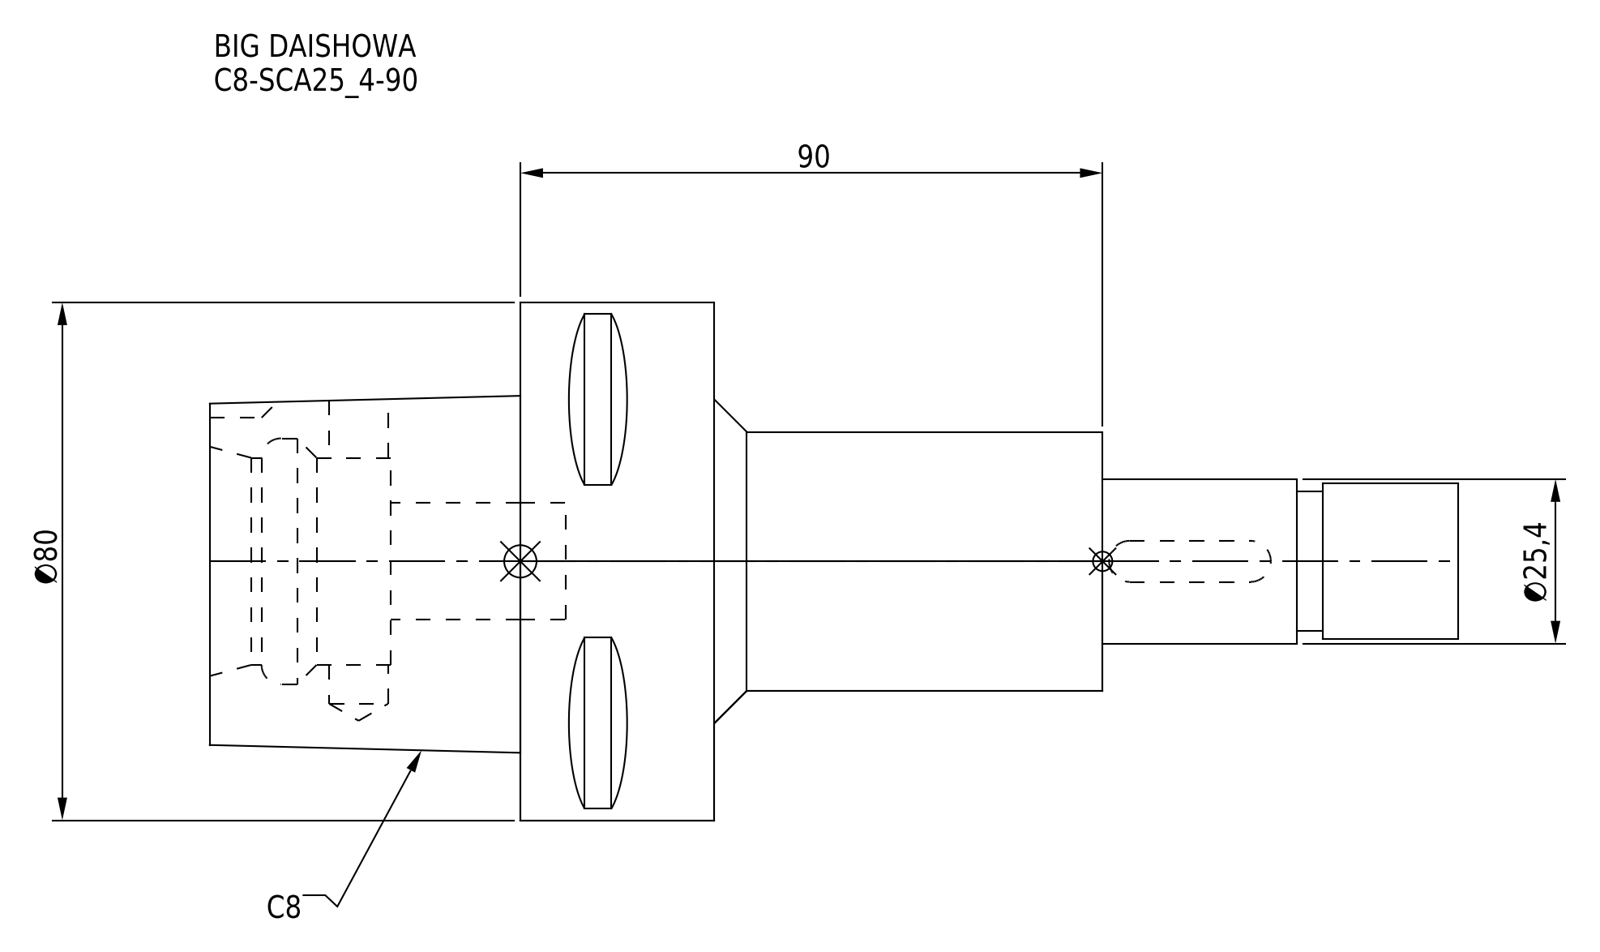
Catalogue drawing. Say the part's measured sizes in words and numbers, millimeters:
The part is named "C8-SCA25_4-90". Its 3-D file was written by "CREO PARAMETRIC BY PTC INC, 2016380 (AUTOMOTIVE_DESIGN)". It is 1 solid with 71 faces: 34 planar, 25 cylindrical and 12 other. Overall it measures 193 by 80 by 80 millimeters. Its volume is 326 799 cubic millimeters and its surface area 42 820 square millimeters. Round holes: 1 of diameter 9.1, 1 of diameter 18, 1 of diameter 32, 1 of diameter 38. Round bosses or shafts: 1 of diameter 80, 1 of diameter 40, 1 of diameter 25.4, 1 of diameter 24, 1 of diameter 21.5. Partial cylindrical surfaces (rounded edges, fillets, slot ends): 2 of radius 3.17, 1 of radius 6. The main face-to-face distances are 30, 78, 48, 138, 90, 60, 55, 20, 110, 50.
